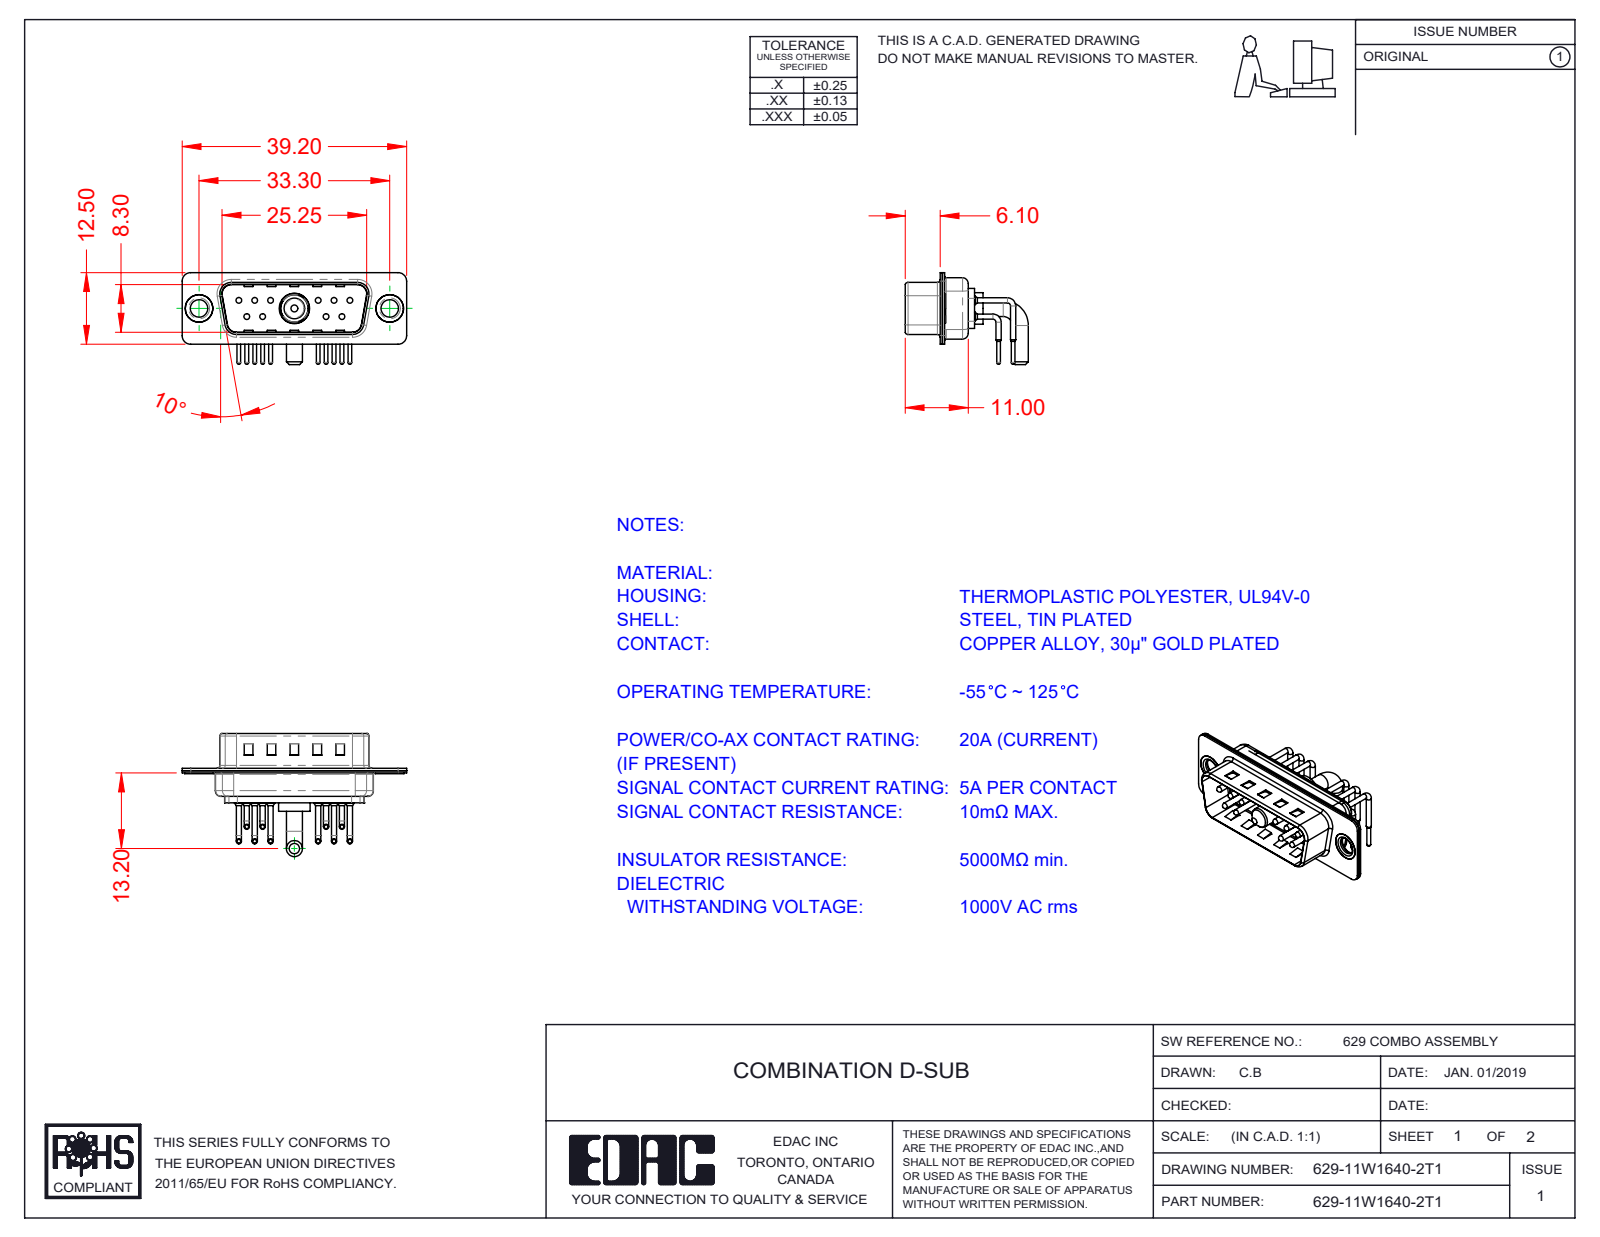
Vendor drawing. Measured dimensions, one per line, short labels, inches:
name: Power Pin_20A RA; 629Combo Housing_11W1; 629Combo Contact Row 2; 629Combo Shell Rear_15 Contacts (+4 more)
written by: SolidWorks 2020 (CONFIG_CONTROL_DESIGN)
unit: in
bodies: 17 solids, 1470 faces (798 planar, 502 cylindrical, 170 other)
size: 1.543 × 0.846 × 0.632
volume: 0.121 in³; area: 7.886 in²
holes: 10× ⌀0.03, 10× ⌀0.063, 10× ⌀0.079, 2× ⌀0.12, 2× ⌀0.157, 2× ⌀0.189, 1× ⌀0.191, 1× ⌀0.209
bosses: 20× ⌀0.035, 10× ⌀0.059, 10× ⌀0.039, 10× ⌀0.026, 2× ⌀0.197, 2× ⌀0.193, 2× ⌀0.14, 2× ⌀0.11
rounds: 16× R0.059, 12× R0.079, 10× R0.04, 8× R0.02, 8× R0.063, 7× R0.039, 4× R0.01, 4× R0.024
face distances: 0.016, 0.031, 0.374, 0.358, 0.343, 0.39, 0.03, 0.22, 0.047, 0.014
hole spacings: 0.124, 0.109, 0.545, 0.436, 0.654, 0.198, 0.198, 0.218
